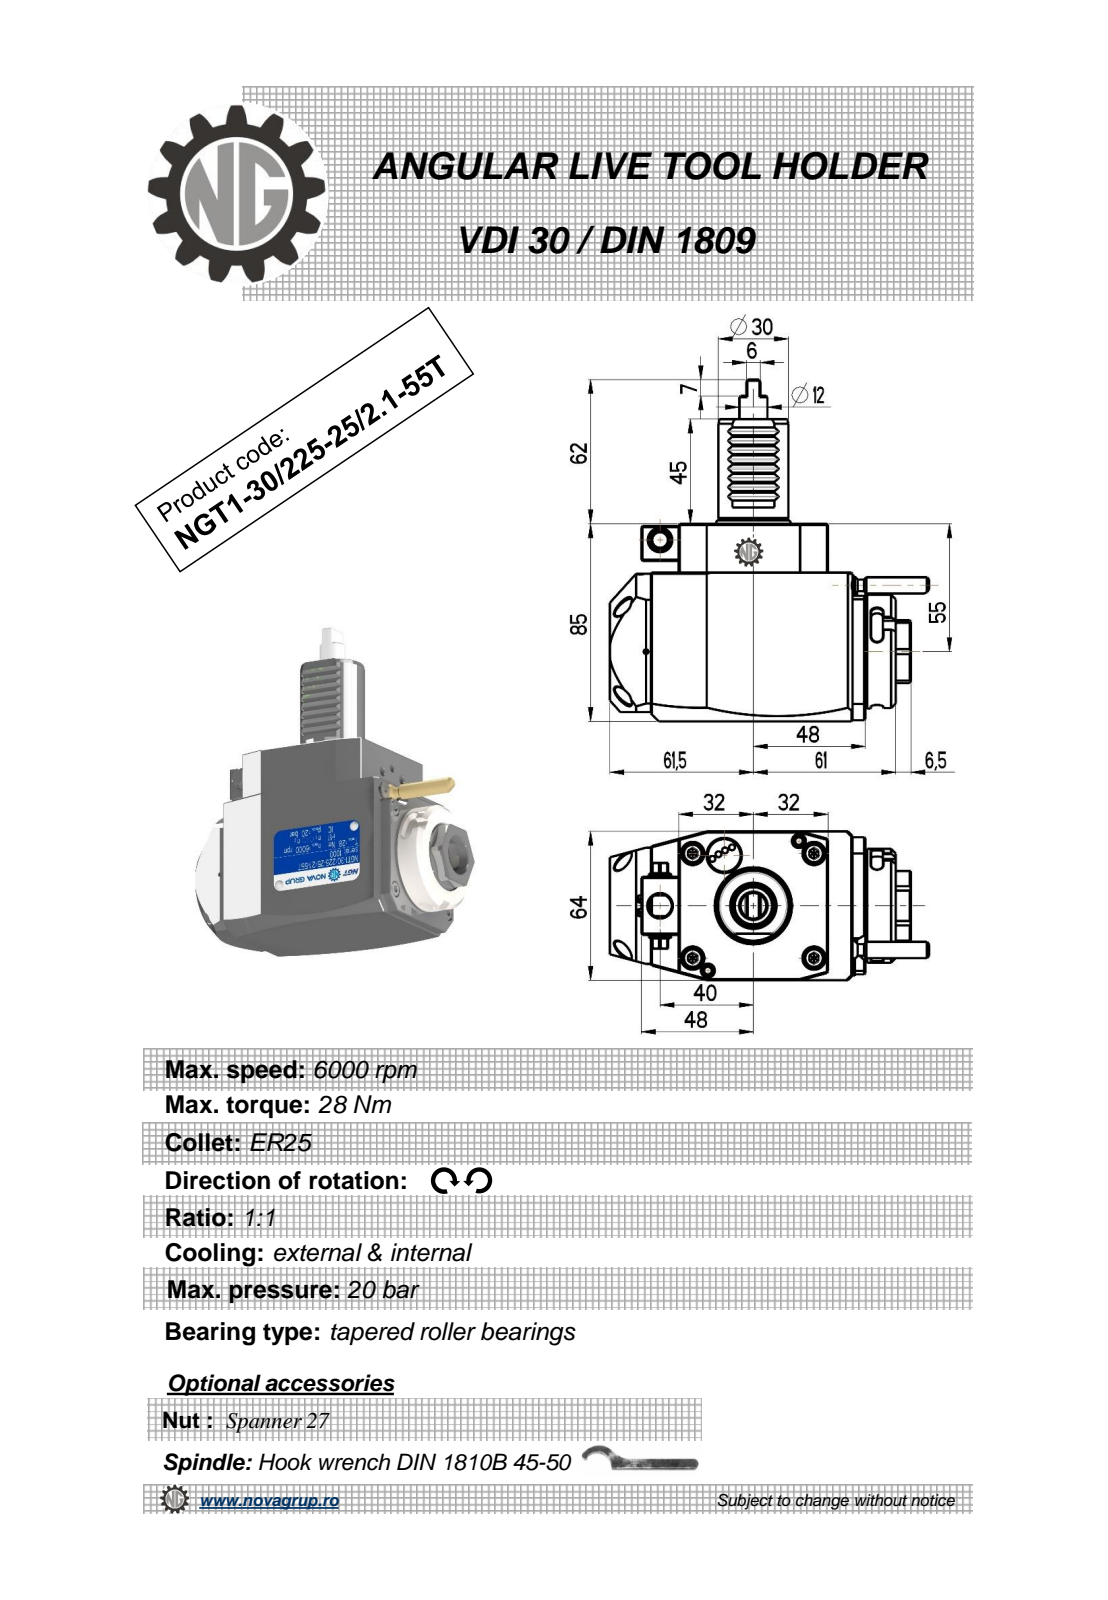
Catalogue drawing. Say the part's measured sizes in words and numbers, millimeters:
The part is named "NGT1_30_225_25_1_1_55T". Its 3-D file was written by "PRO/ENGINEER BY PARAMETRIC TECHNOLOGY CORPORATION, 2010280 (CONFIG_CONTROL_DESIGN)". It is 1 solid with 337 faces: 183 planar, 84 cylindrical and 70 other. Overall it measures 147 by 136.88 by 64 millimeters. Its volume is 548 333 cubic millimeters and its surface area 49 072 square millimeters. Round holes: 1 of diameter 2.5, 1 of diameter 3, 1 of diameter 9.5, 1 of diameter 10, 1 of diameter 18. Round bosses or shafts: 2 of diameter 8, 1 of diameter 49, 1 of diameter 42, 1 of diameter 30, 1 of diameter 12, 1 of diameter 10, 1 of diameter 7, 1 of diameter 5. Partial cylindrical surfaces (rounded edges, fillets, slot ends): 8 of radius 0.3, 6 of radius 2.5, 2 of radius 0.8, 2 of radius 180, 1 of radius 3.85, 1 of radius 4.25, 1 of radius 4.5, 1 of radius 15. The main face-to-face distances are 64, 85, 16, 80, 109.5, 13, 21, 29, 122.5, 93.5. The hole center spacings are 26.17, 34.25, 46.5.
